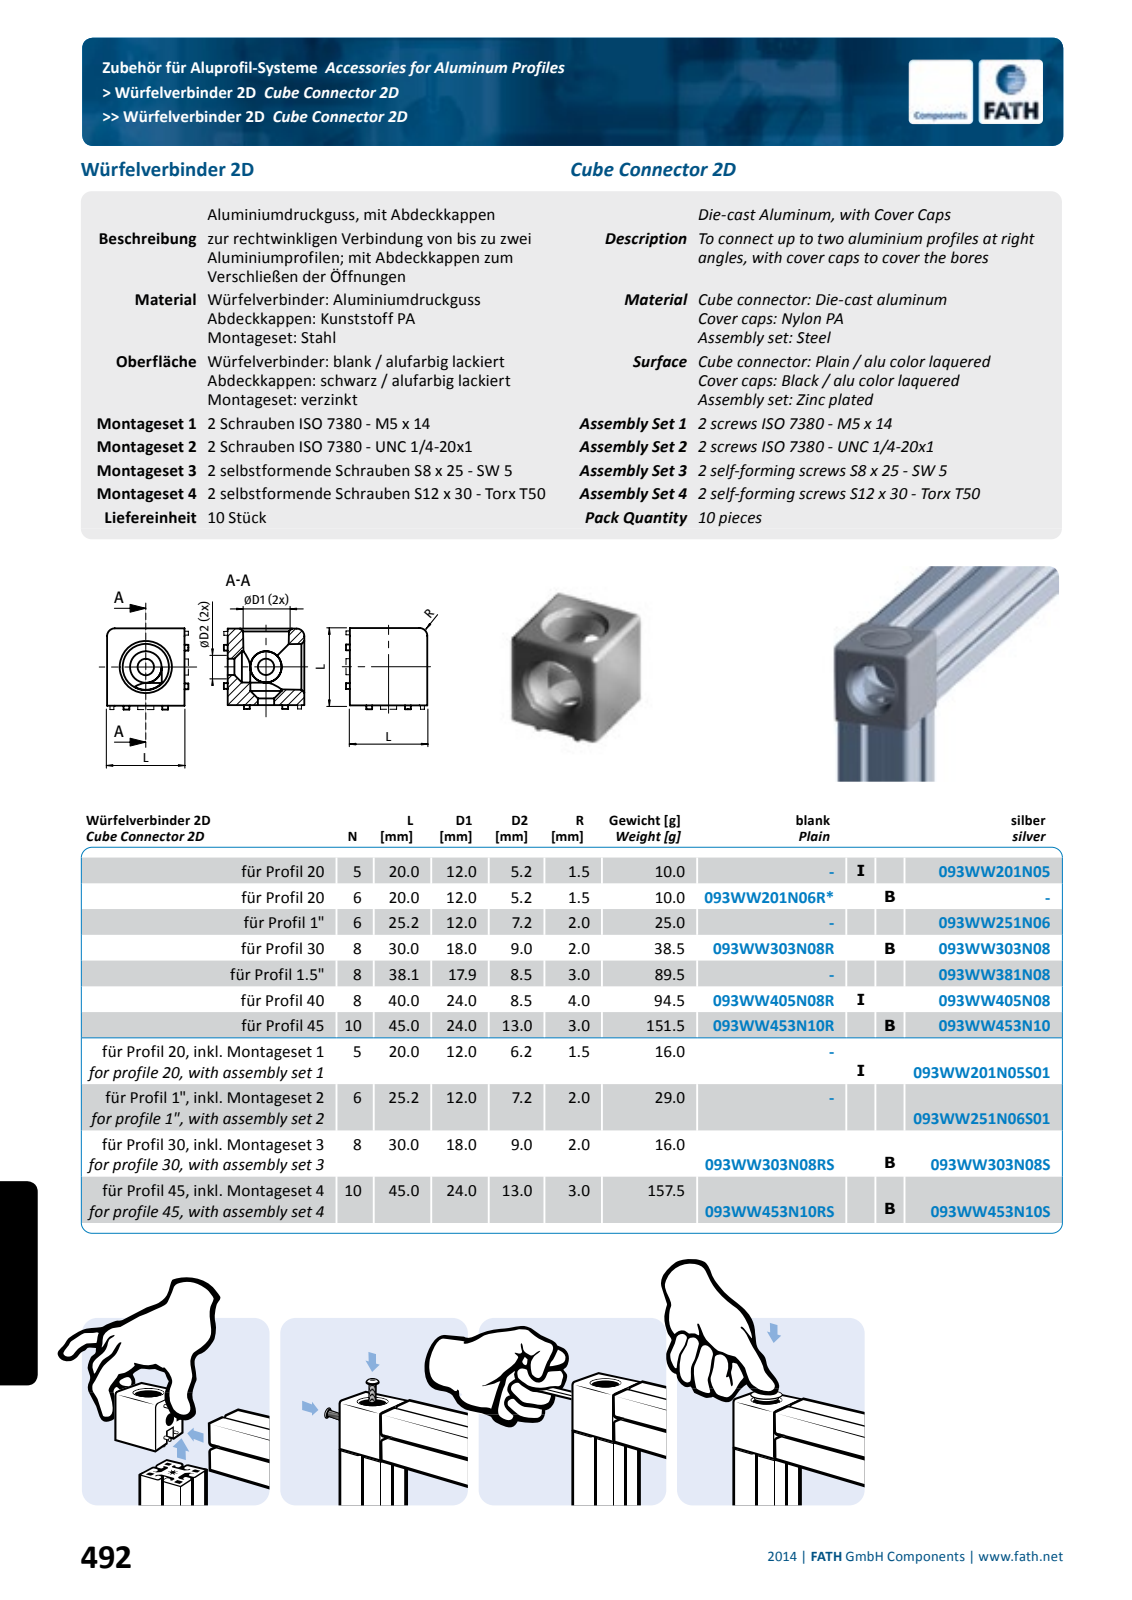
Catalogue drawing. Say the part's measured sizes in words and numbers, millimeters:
The part is named "fath_093ww453n10". Its 3-D file was written by "Spatial InterOp 3D (automotive_design)". It is 1 solid with 78 faces: 19 planar, 9 cylindrical and 50 other. Overall it measures 49 by 49 by 45 millimeters. Its volume is 64 756 cubic millimeters and its surface area 15 371 square millimeters. Round holes: 2 of diameter 13. Partial cylindrical surfaces (rounded edges, fillets, slot ends): 5 of radius 3. The main face-to-face distances are 45, 7, 38, 17.25, 27.75, 10.5, 4, 11, 49.
